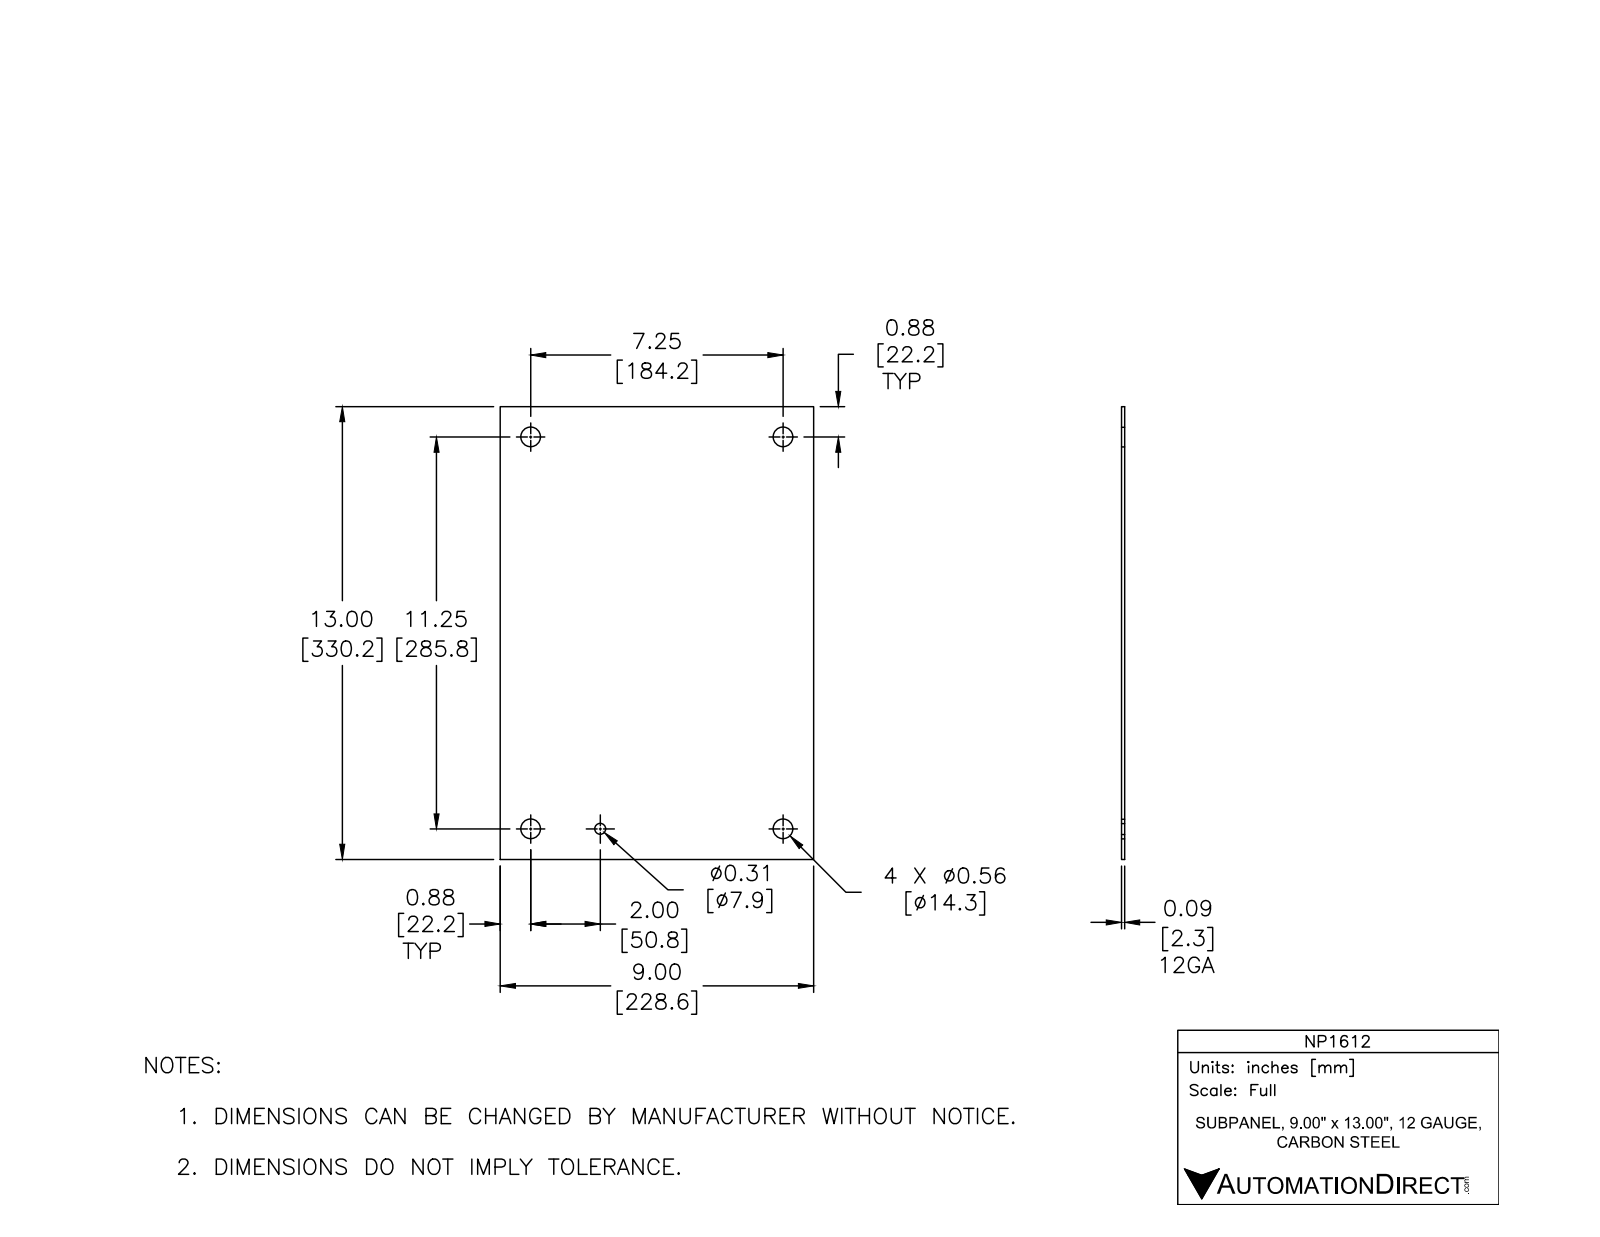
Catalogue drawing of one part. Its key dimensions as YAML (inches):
part_name: "NP1612"
step_written_by: "Autodesk Inventor 2012 (AUTOMOTIVE_DESIGN)"
units: inches
bodies: {solids: 1, faces: 11, planar: 6, cylindrical: 5, other: 0}
overall_size: [13, 9, 0.094]
volume: 10.87
surface_area: 236.7
round_holes:
  - {diameter: 0.563, count: 4}
  - {diameter: 0.31, count: 1}
face_to_face_distances: [0.094, 9, 13]
hole_center_spacings: [7.25, 2, 5.25, 11.25, 11.25, 11.426, 12.415, 13.384]
